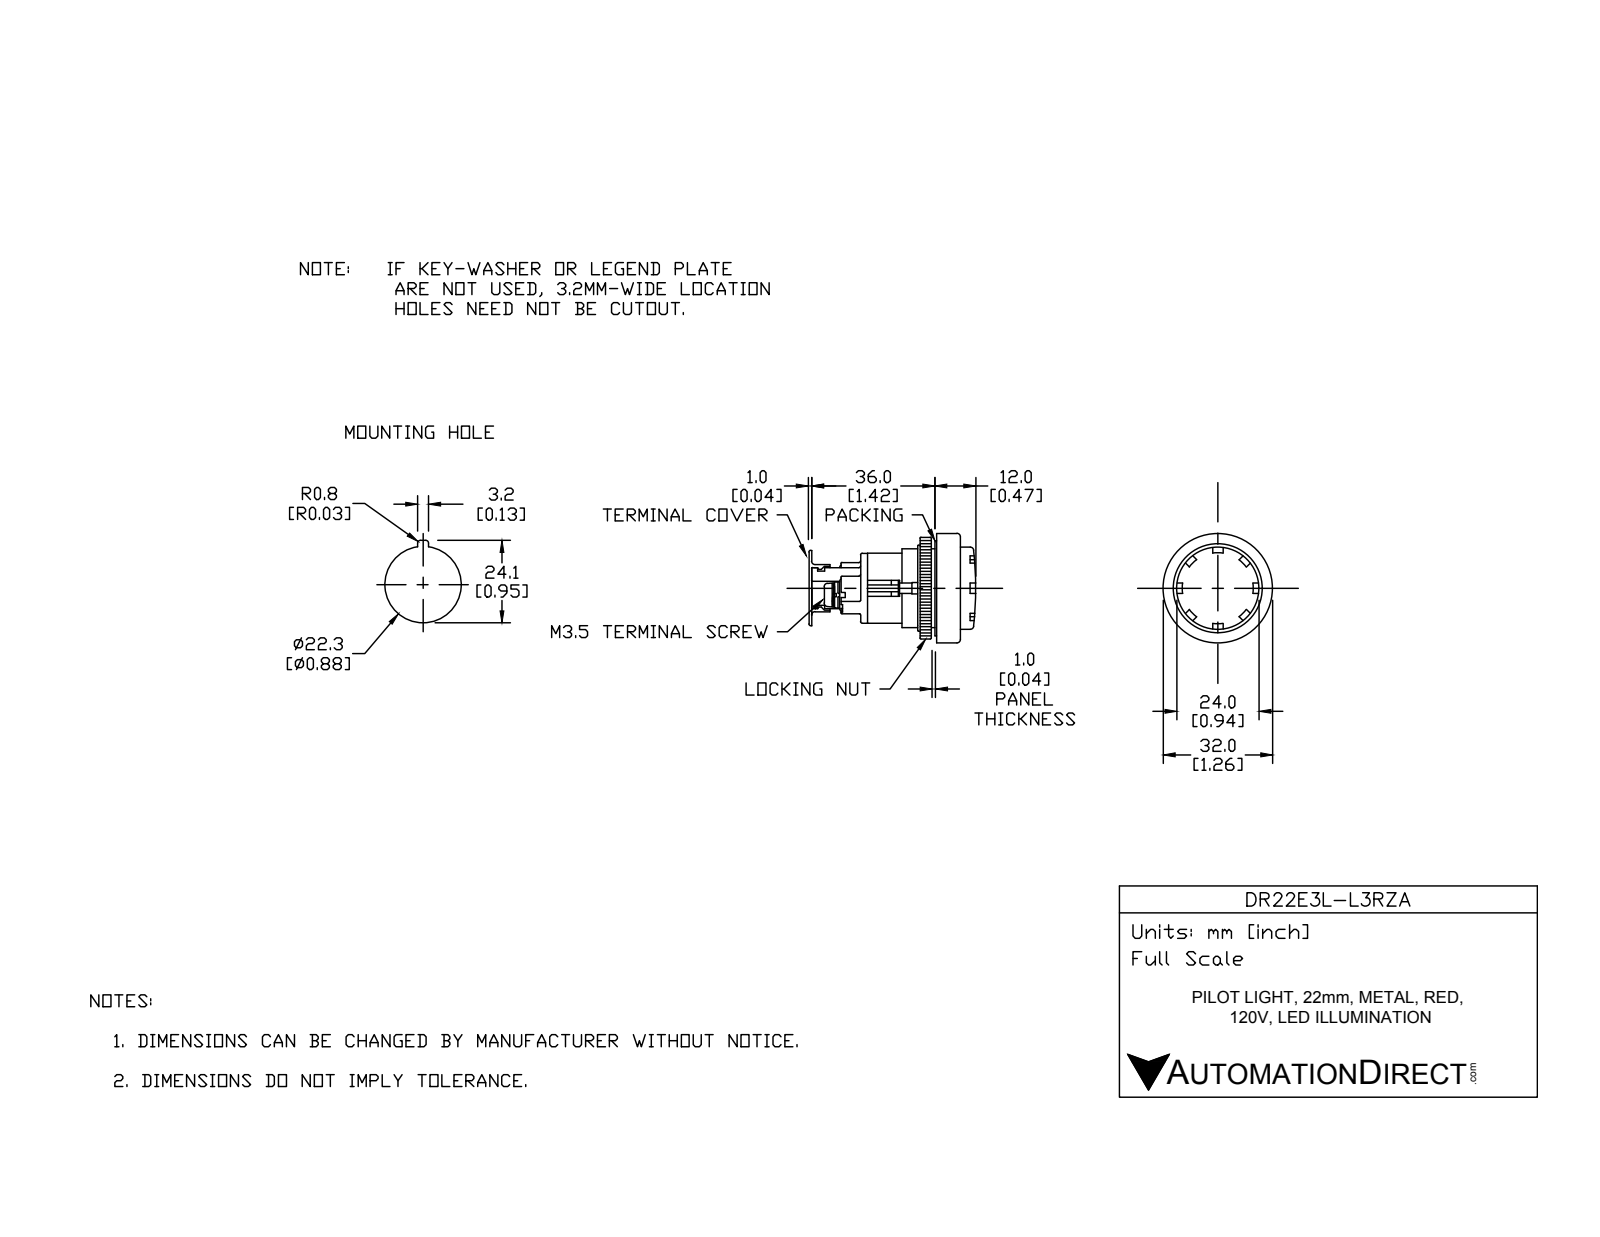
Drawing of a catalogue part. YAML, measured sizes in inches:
part_name: "DR22E3L-L3RZA"
step_written_by: "SolidWorks 2017 (AUTOMOTIVE_DESIGN)"
units: inches
bodies: {solids: 12, faces: 232, planar: 165, cylindrical: 51, other: 16}
overall_size: [2.913, 1.26, 1.26]
volume: 2.435
surface_area: 28.15
round_holes:
  - {diameter: 0.866, count: 1}
  - {diameter: 0.886, count: 1}
  - {diameter: 0.984, count: 1}
  - {diameter: 1.181, count: 1}
round_bosses_or_shafts:
  - {diameter: 0.217, count: 2}
  - {diameter: 1.26, count: 1}
  - {diameter: 1.169, count: 1}
  - {diameter: 1.161, count: 1}
  - {diameter: 1.063, count: 1}
  - {diameter: 0.858, count: 1}
partial_cylinders:
  - {radius: 0.02, count: 14}
  - {radius: 0.128, count: 4}
  - {radius: 0.039, count: 1}
  - {radius: 0.197, count: 1}
face_to_face_distances: [0.748, 1.181, 1.055, 0.039, 0.157, 0.236, 0.819, 0.433, 1.28, 0.063]
